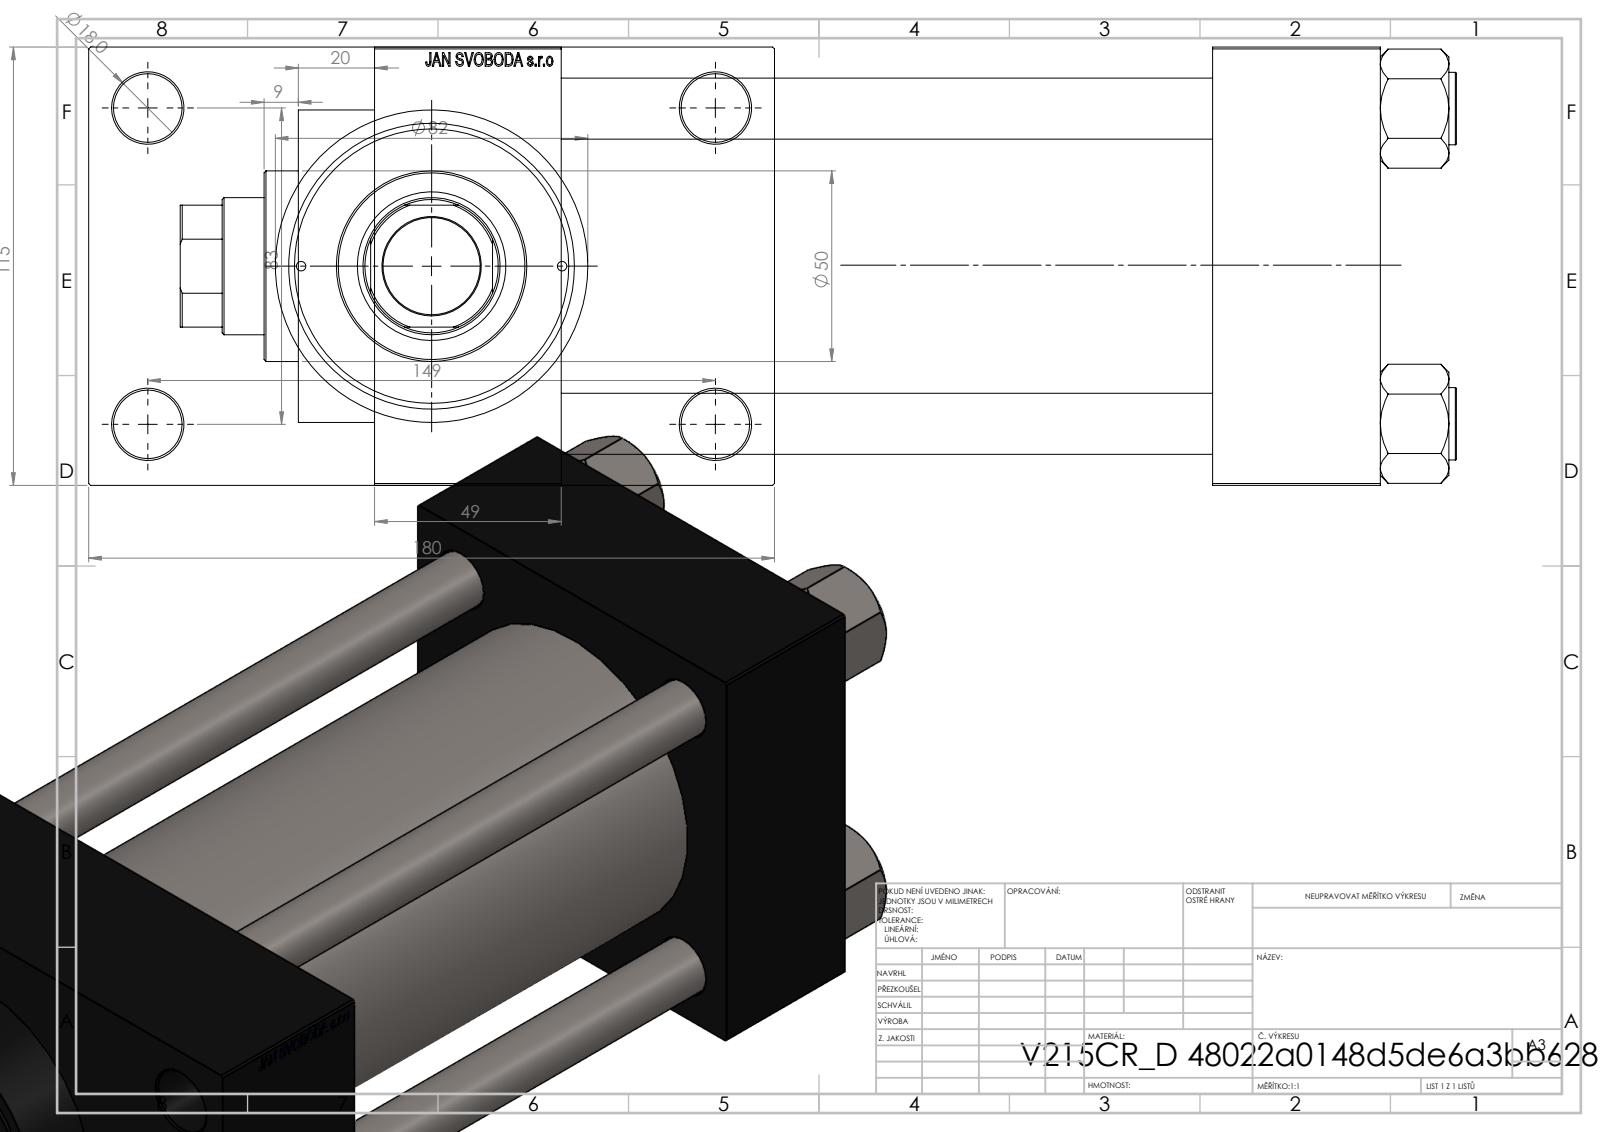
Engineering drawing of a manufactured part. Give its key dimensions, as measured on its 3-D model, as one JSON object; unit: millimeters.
{"part_name": "NUT_M5_D; V215CR_D_TYCINKA; V215CR_D_Body; V215CR_VCP_D (+1 more)", "step_written_by": "SolidWorks 2019 (CONFIG_CONTROL_DESIGN)", "units": "millimeters", "bodies": {"solids": 11, "faces": 1159, "planar": 547, "cylindrical": 92, "other": 520}, "overall_size": [335, 180, 115], "volume_mm3": 2253000, "surface_area_mm2": 384222, "round_holes": [[16, 4], [18, 4], [2.5, 2], [7, 2], [26.44, 2], [35, 2], [25.5, 1], [36, 1], [39, 1], [61, 1], [72, 1], [80, 1]], "round_bosses_or_shafts": [[19, 4], [86, 1], [82, 1], [50, 1]], "partial_cylinders_radius": [[17.5, 1]], "face_to_face_distances": [115, 171, 220, 49, 44, 215, 264, 32.5, 147.5, 180], "hole_center_spacings": [33.15, 41.96, 57.81, 58.48, 82.7, 85.28, 86.17, 89.24]}
